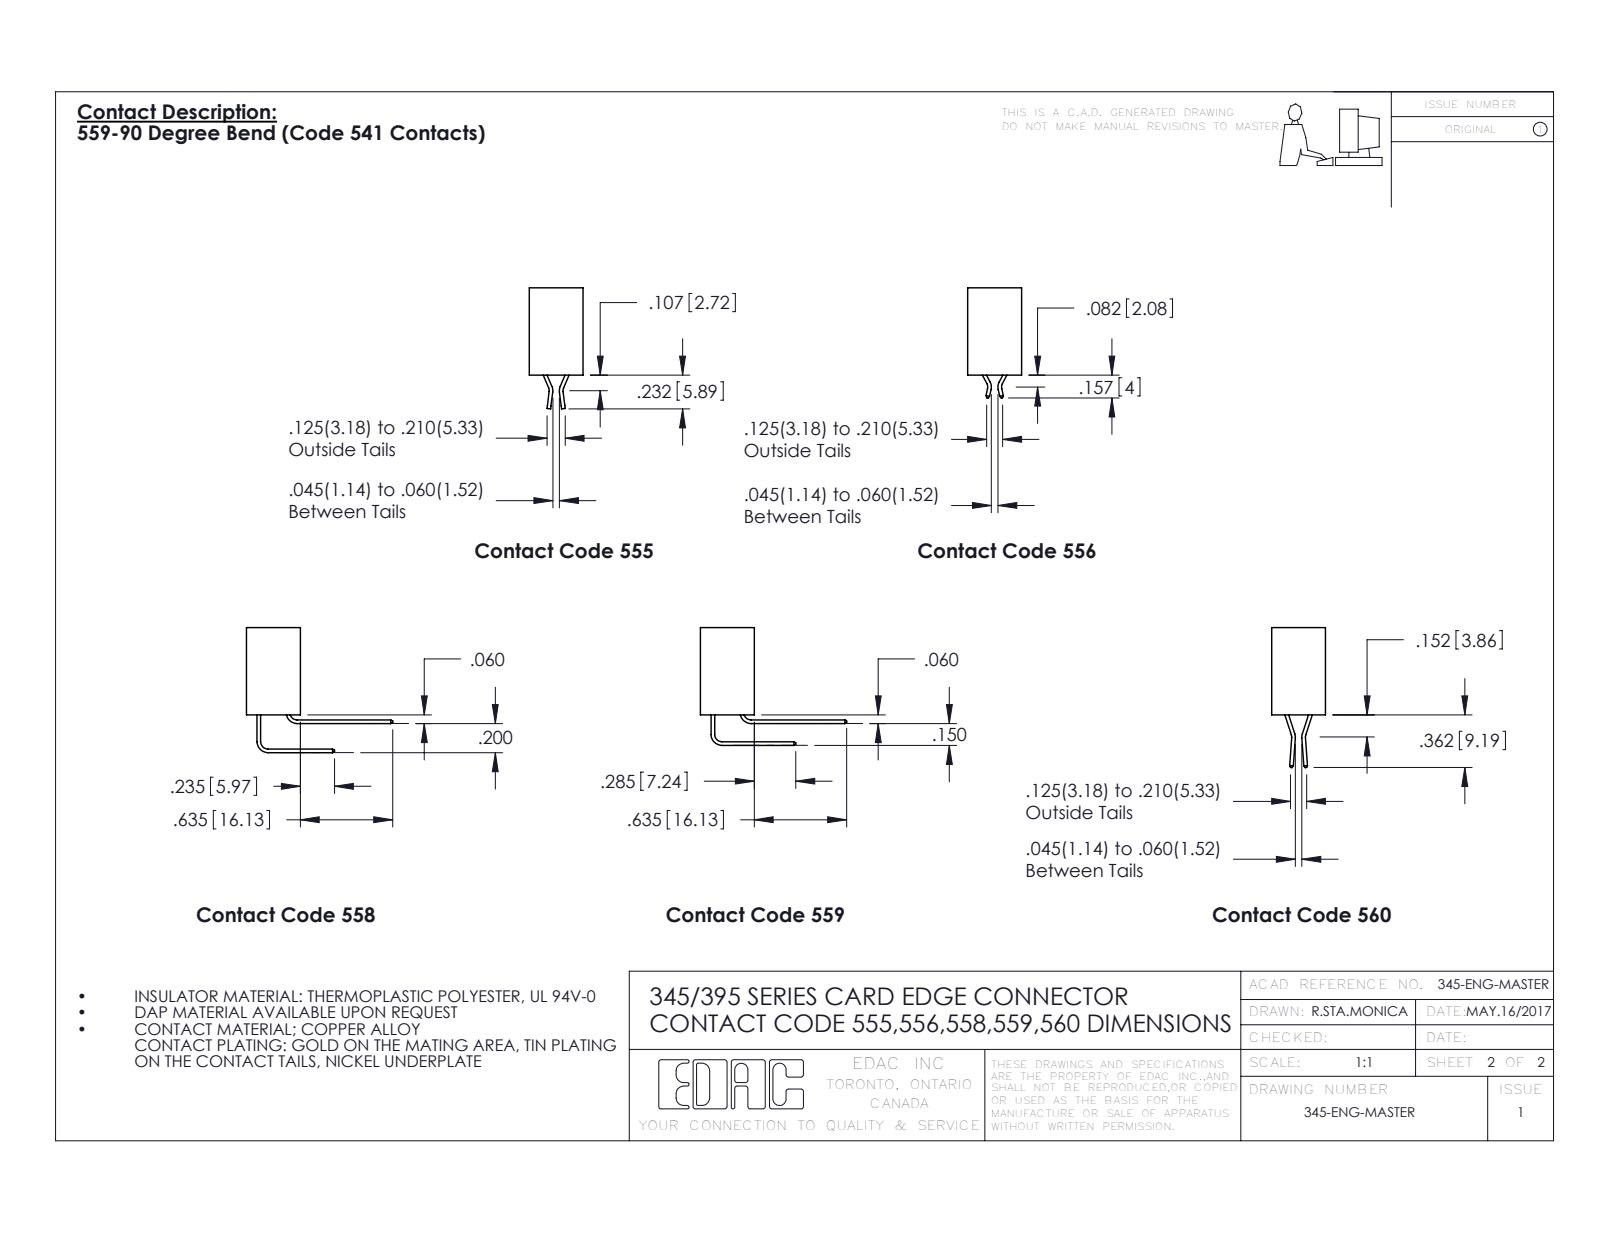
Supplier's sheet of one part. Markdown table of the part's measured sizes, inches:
| quantity | value |
| --- | --- |
| part name | 395-027-559-112; 345-292-001_558 559 Tail - 1; 345 Part_Flush Mounting Lugs - Side Mount |
| STEP written by | SolidWorks 2016 (CONFIG_CONTROL_DESIGN) |
| units | inches |
| bodies | 28 solids, 1746 faces (1214 planar, 532 cylindrical, 0 other) |
| overall size | 3.535 × 1.005 × 0.659 |
| volume | 0.513 in³ |
| surface area | 17.6 in² |
| round holes (diameter × count) | 0.128 × 2, 0.064 × 1 |
| partial cylindrical surfaces (radius × count) | 0.006 × 54, 0.01 × 22, 0.007 × 6, 0.031 × 6, 0.026 × 3, 0.031 × 2, 0.04 × 2, 0.014 × 1 |
| main face-to-face distances | 0.298, 0.072, 0.37, 0.2, 0.098, 0.272, 0.025, 0.225, 0.149, 0.072 |
| hole center spacings | 3.275 |
